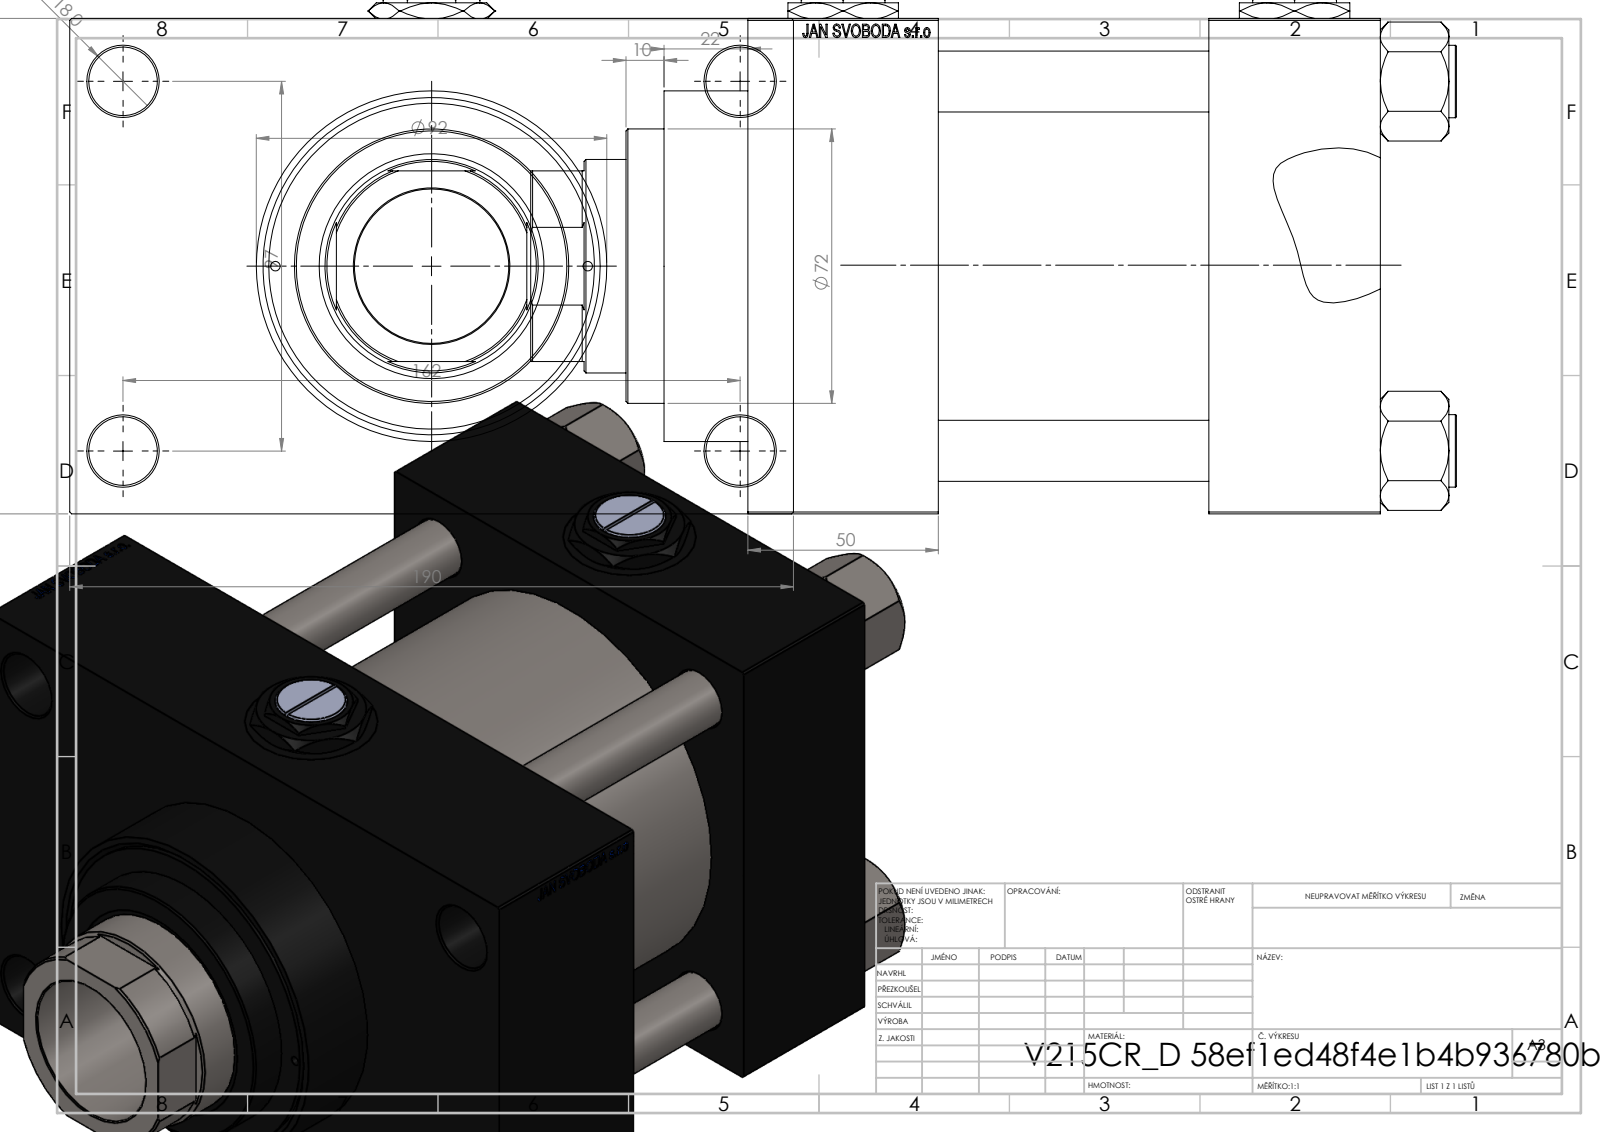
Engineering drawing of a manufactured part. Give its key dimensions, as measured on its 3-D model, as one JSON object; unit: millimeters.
{"part_name": "NUT_M5_D; V215CR_VCP_D; V215_VC_A; V215CR_D_TYCINKA (+2 more)", "step_written_by": "SolidWorks 2019 (CONFIG_CONTROL_DESIGN)", "units": "millimeters", "bodies": {"solids": 13, "faces": 1260, "planar": 595, "cylindrical": 103, "other": 562}, "overall_size": [243, 190, 137], "volume_mm3": 2613000, "surface_area_mm2": 369127, "round_holes": [[16, 4], [18, 4], [26.44, 4], [35, 4], [7, 3], [2.5, 2], [40.5, 1], [56, 1], [59, 1], [76, 1], [85.5, 1], [100, 1]], "round_bosses_or_shafts": [[19, 4], [106, 1], [92, 1], [72, 1]], "partial_cylinders_radius": [[27, 1]], "face_to_face_distances": [130, 116, 50, 45, 71, 121, 166, 30, 160, 20], "hole_center_spacings": [32.55, 49.02, 62.87, 68.52, 94.41, 96.9, 101.73, 102.27]}
